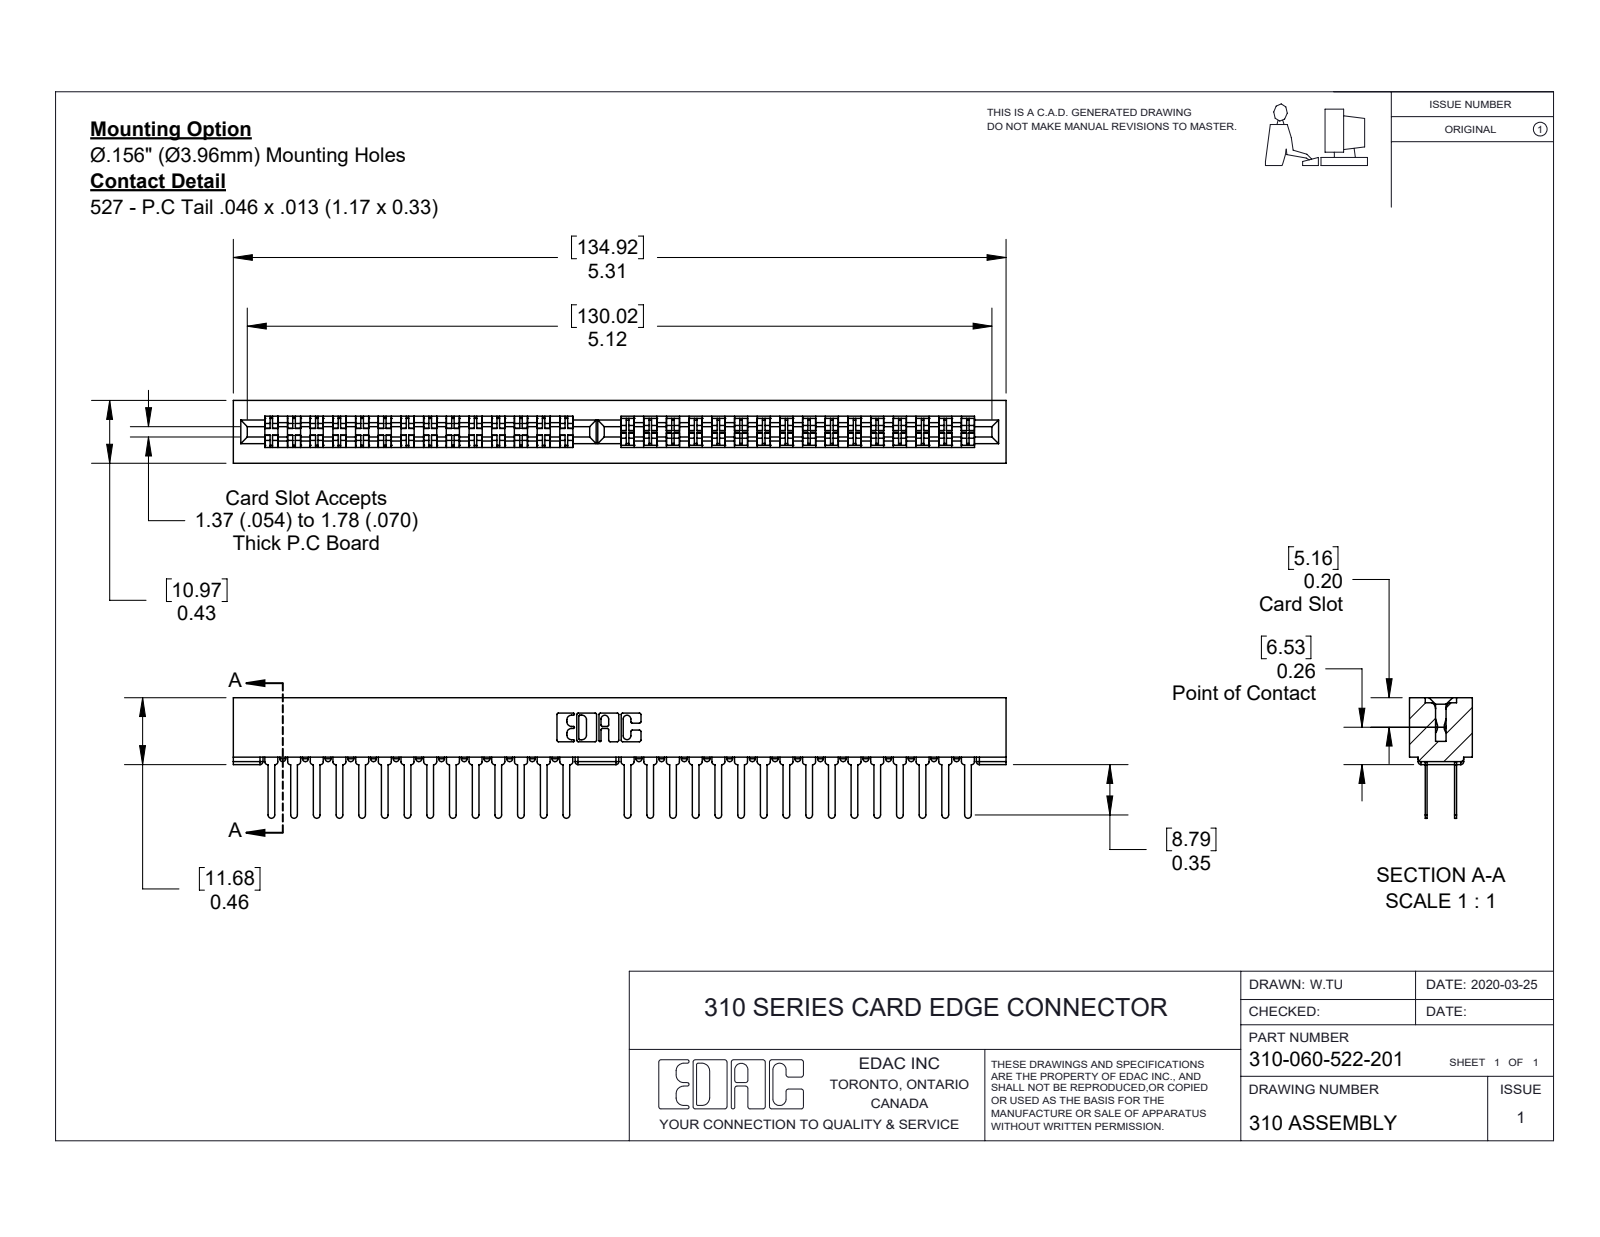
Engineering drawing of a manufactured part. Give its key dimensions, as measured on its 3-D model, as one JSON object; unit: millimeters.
{"part_name": "307-290-001_522; 310 Part_No Mounting Lugs; 310-060-522-201", "step_written_by": "SolidWorks 2016 (CONFIG_CONTROL_DESIGN)", "units": "millimeters", "bodies": {"solids": 61, "faces": 2918, "planar": 1940, "cylindrical": 914, "other": 64}, "overall_size": [134.93, 21.06, 10.97], "volume_mm3": 12140, "surface_area_mm2": 17620, "partial_cylinders_radius": [[0.51, 158], [0.58, 30], [0.25, 22], [0.17, 6], [0.8, 6], [0.3, 4], [0.64, 4], [1.19, 4]], "face_to_face_distances": [2.76, 8.22, 0.33, 0.38, 4.75, 10.98, 3.14, 7.84, 5.08, 5.46]}
